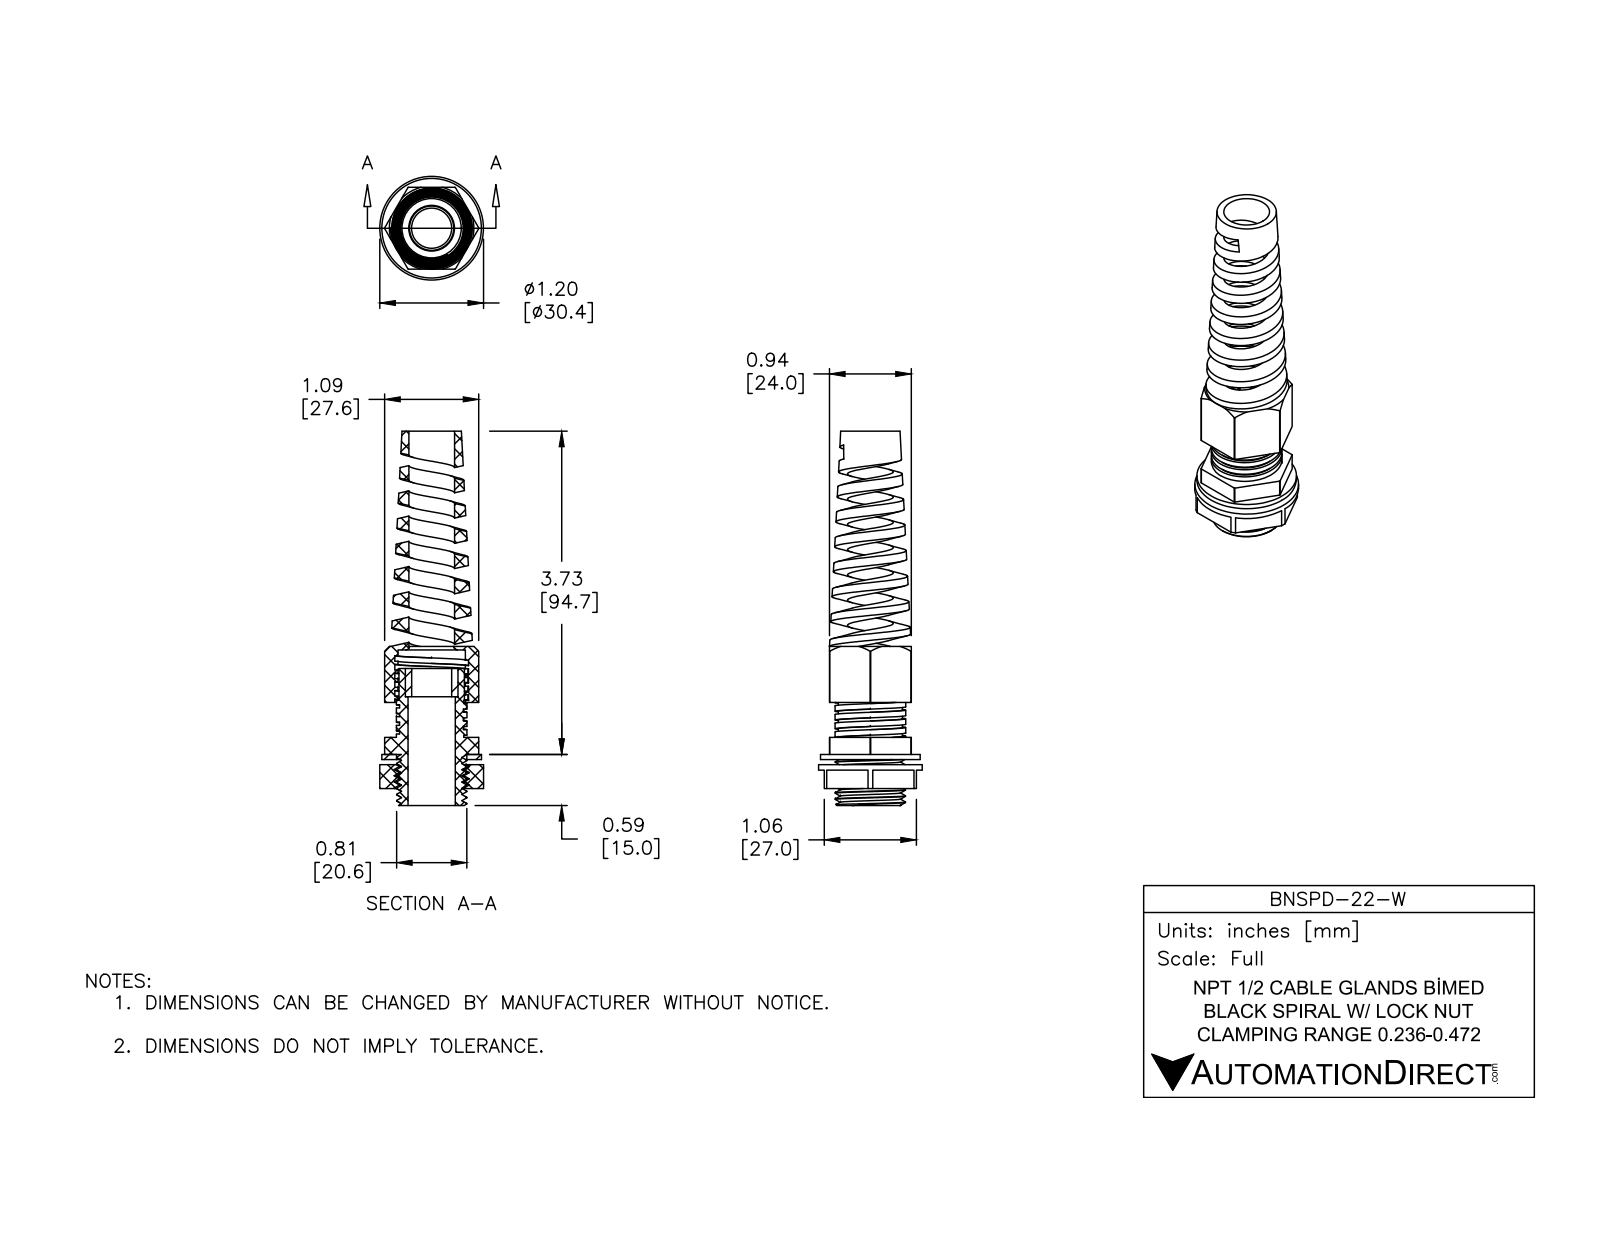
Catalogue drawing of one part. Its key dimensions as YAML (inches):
part_name: "BNSPBX-22-W"
step_written_by: "SolidWorks 2015 (CONFIG_CONTROL_DESIGN)"
units: inches
bodies: {solids: 5, faces: 241, planar: 105, cylindrical: 97, other: 39}
overall_size: [4.32, 1.197, 1.197]
volume: 1.133
surface_area: 32.67
round_holes:
  - {diameter: 0.462, count: 1}
  - {diameter: 0.528, count: 1}
  - {diameter: 0.546, count: 1}
  - {diameter: 0.606, count: 1}
  - {diameter: 0.753, count: 1}
  - {diameter: 0.778, count: 1}
  - {diameter: 0.811, count: 1}
round_bosses_or_shafts:
  - {diameter: 1.197, count: 1}
  - {diameter: 1.15, count: 1}
  - {diameter: 0.815, count: 1}
  - {diameter: 0.81, count: 1}
  - {diameter: 0.756, count: 1}
partial_cylinders:
  - {radius: 0.543, count: 1}
face_to_face_distances: [0.944, 0.039, 0.059, 1.004, 0.098, 1.305, 0.059, 0.276, 0.315, 0.374]
